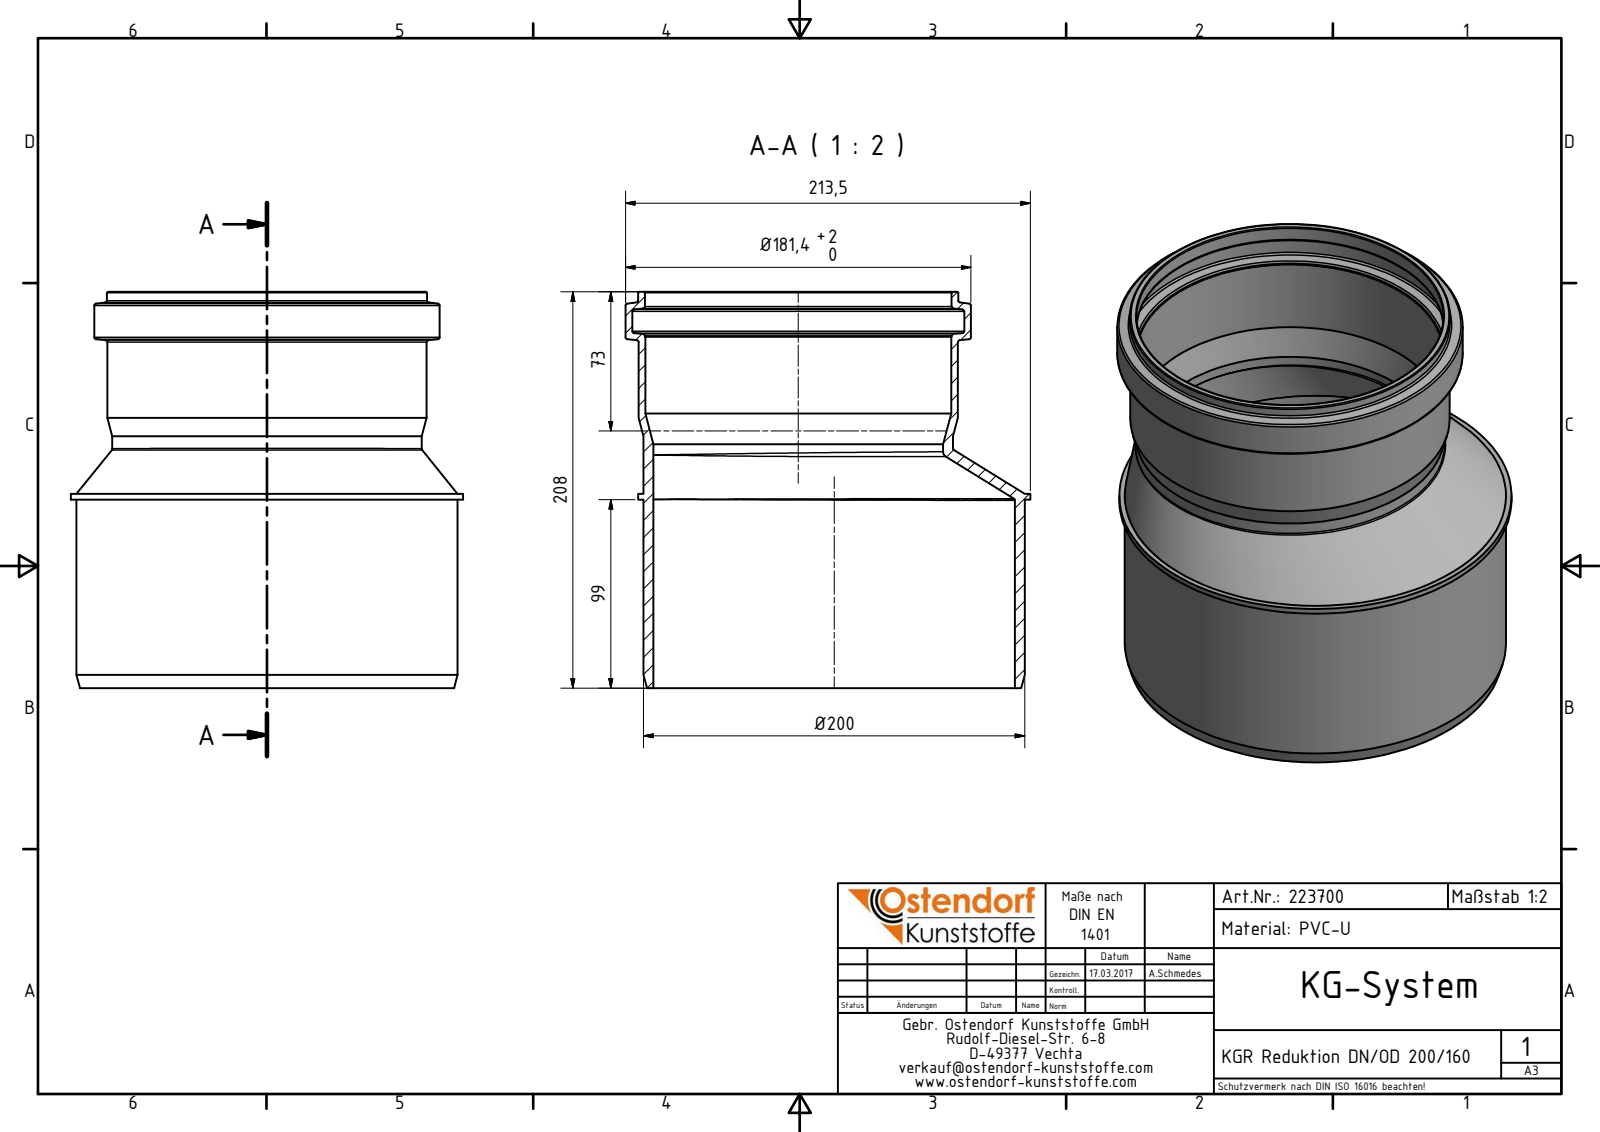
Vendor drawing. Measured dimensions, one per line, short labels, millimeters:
name: 223700 KGR Reduktion DN_OD 200_160
written by: Autodesk Inventor 2016 (AUTOMOTIVE_DESIGN)
unit: mm
bodies: 1 solid, 39 faces (5 planar, 12 cylindrical, 22 other)
size: 212.55 × 208 × 206
volume: 604 121 mm³; area: 265 606 mm²
holes: 1× ⌀152.1, 1× ⌀160.7, 1× ⌀161.1, 1× ⌀174.4, 1× ⌀189.8
bosses: 1× ⌀206, 1× ⌀200.2, 1× ⌀181.4, 1× ⌀168.1, 1× ⌀167.7, 1× ⌀162.5
face distances: 99, 102, 3, 208, 109, 106, 184.39, 85.39, 82.39, 23.61
hole spacings: 18.85
